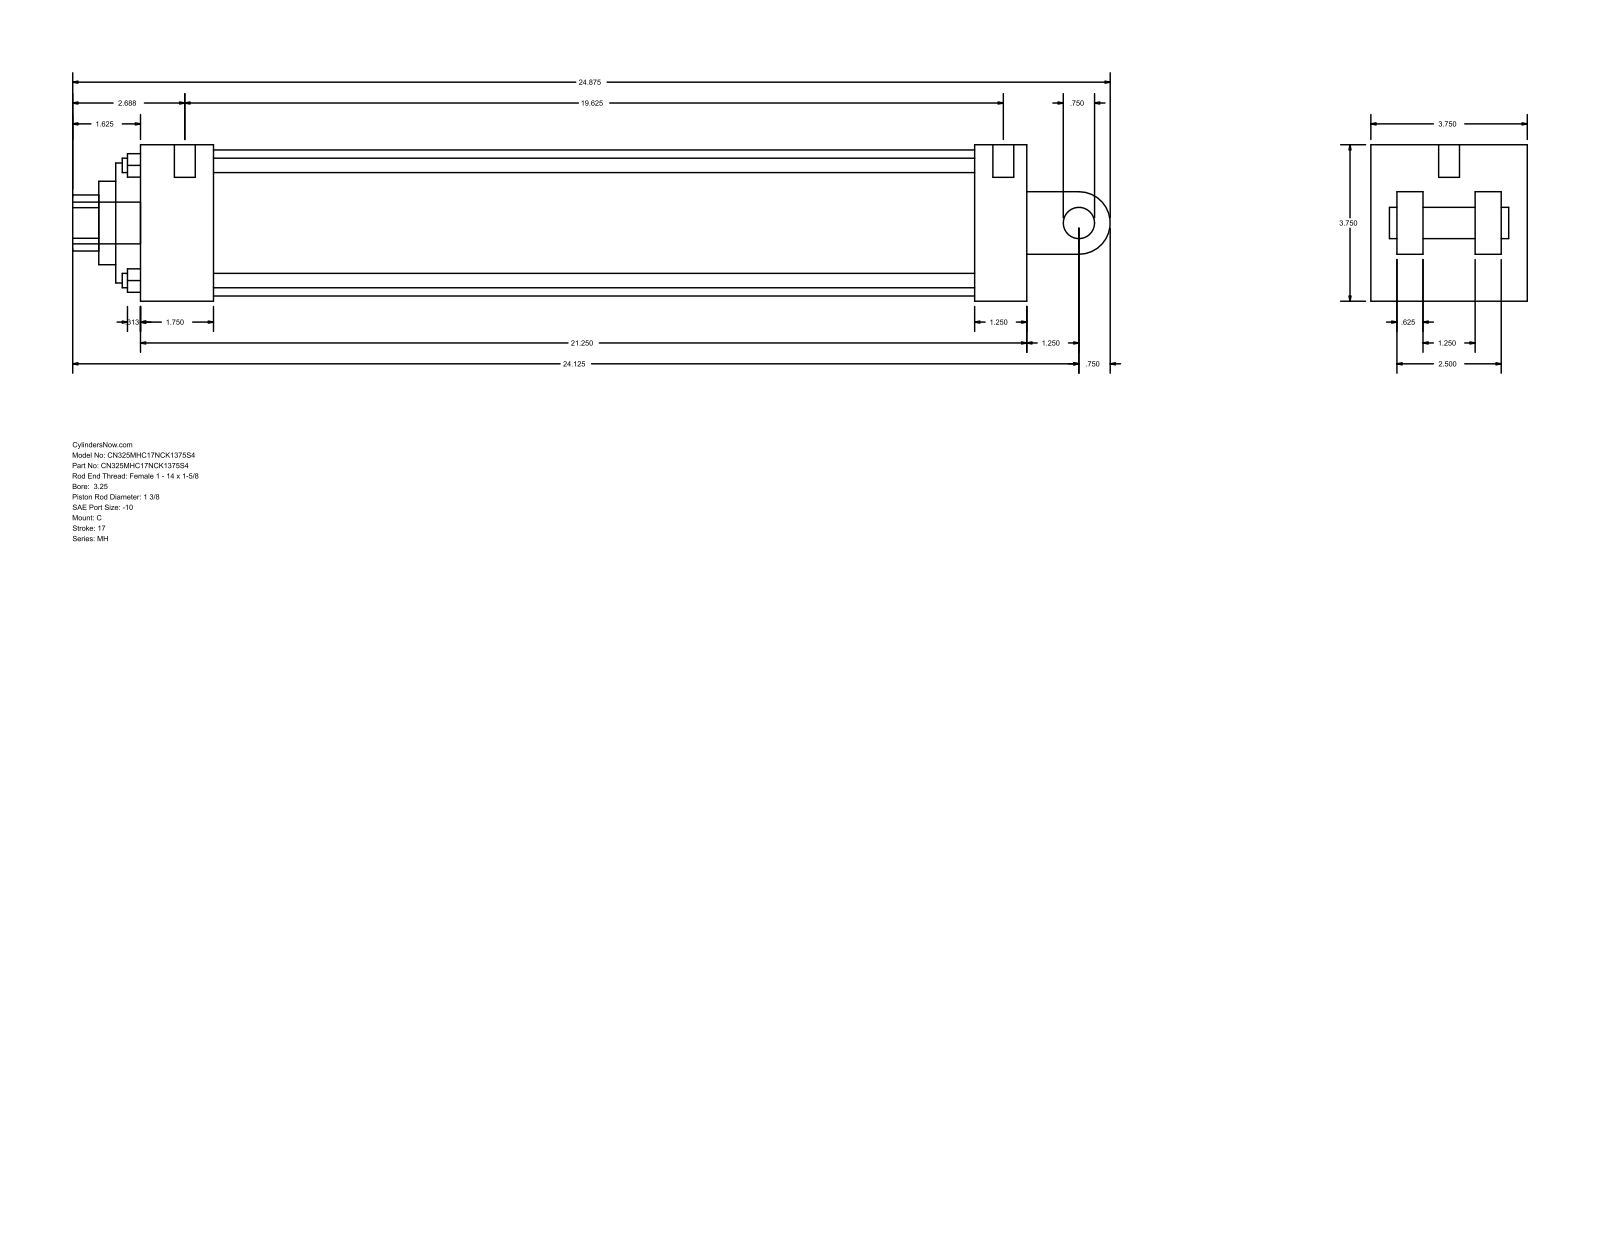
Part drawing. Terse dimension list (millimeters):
name: MH_C__0325_1.375
written by: GSSL Pune (CONFIG_CONTROL_DESIGN)
unit: mm
bodies: 0 solids, 101 faces (71 planar, 30 cylindrical, 0 other)
size: 631.83 × 95.25 × 95.25
holes: 4× ⌀8.76, 2× ⌀5.56, 1× ⌀12.7, 1× ⌀34.92, 1× ⌀50.8, 1× ⌀73.03, 1× ⌀88.9
bosses: 2× ⌀5.56, 1× ⌀25.4, 1× ⌀19.05, 1× ⌀12.7
rounds: 1× R17.06, 1× R19.05
face distances: 95.24, 15.87, 539.75, 63.5, 31.74, 79.37, 47.63, 44.45, 508, 463.55
hole spacings: 49.57, 70.1, 99.14, 4.76
